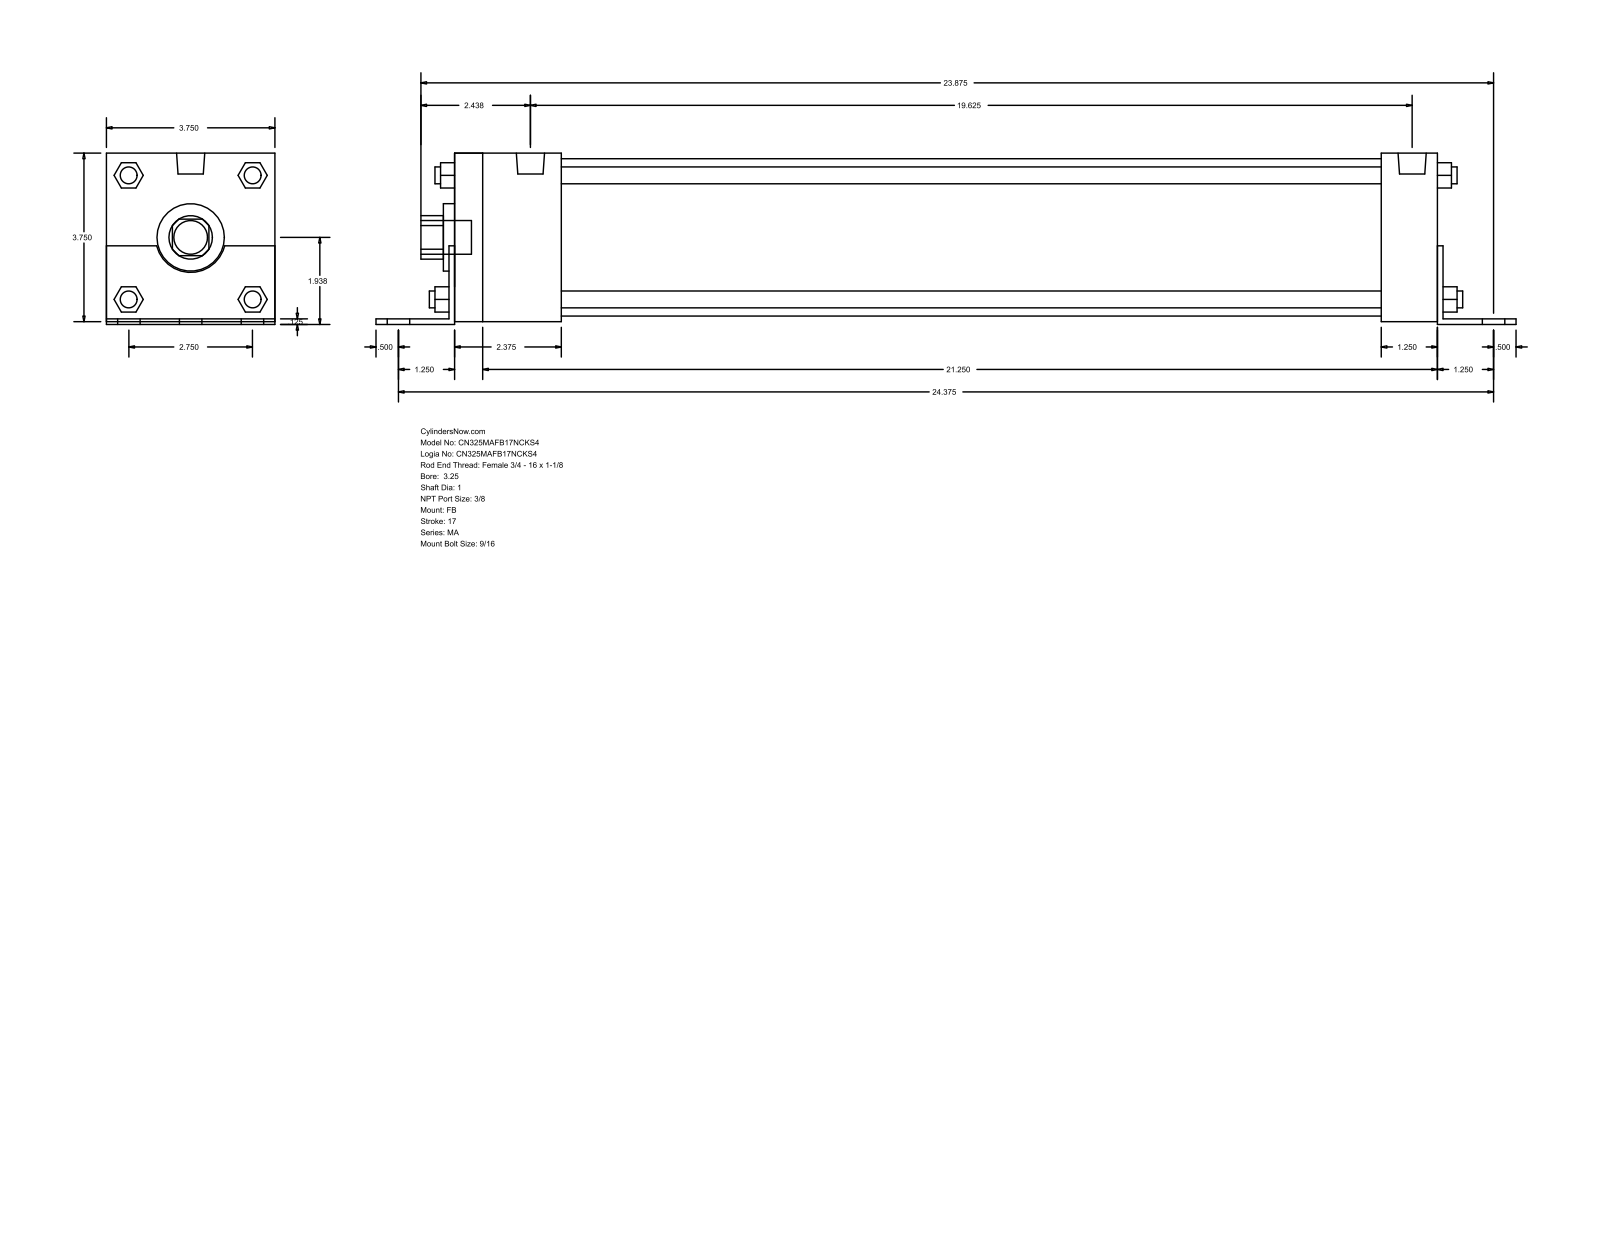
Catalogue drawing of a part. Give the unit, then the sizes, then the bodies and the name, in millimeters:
Units: millimetres
Overall size (bounding box): 644.52 × 96.84 × 95.25
Round holes (diameter × count): ⌀25.4 ×1, ⌀38.1 ×1, ⌀88.9 ×1
Round bosses / shafts (diameter × count): ⌀14.29 ×6, ⌀11.11 ×4, ⌀9.53 ×4, ⌀15.93 ×2, ⌀19.05 ×1
Partial cylindrical surfaces — rounded edges, fillets, slot ends (radius × count): R12.29 ×1, R19.81 ×1
Main face-to-face distances: 95.24, 3.17, 1.59, 96.83, 1.58, 93.66, 3.18, 555.62, 561.97, 558.8
Bodies: 0 solids, 140 faces (105 planar, 35 cylindrical, 0 other)
Part name (STEP PRODUCT): MA_FB__0325_1
STEP written by: GSSL Pune (CONFIG_CONTROL_DESIGN)
